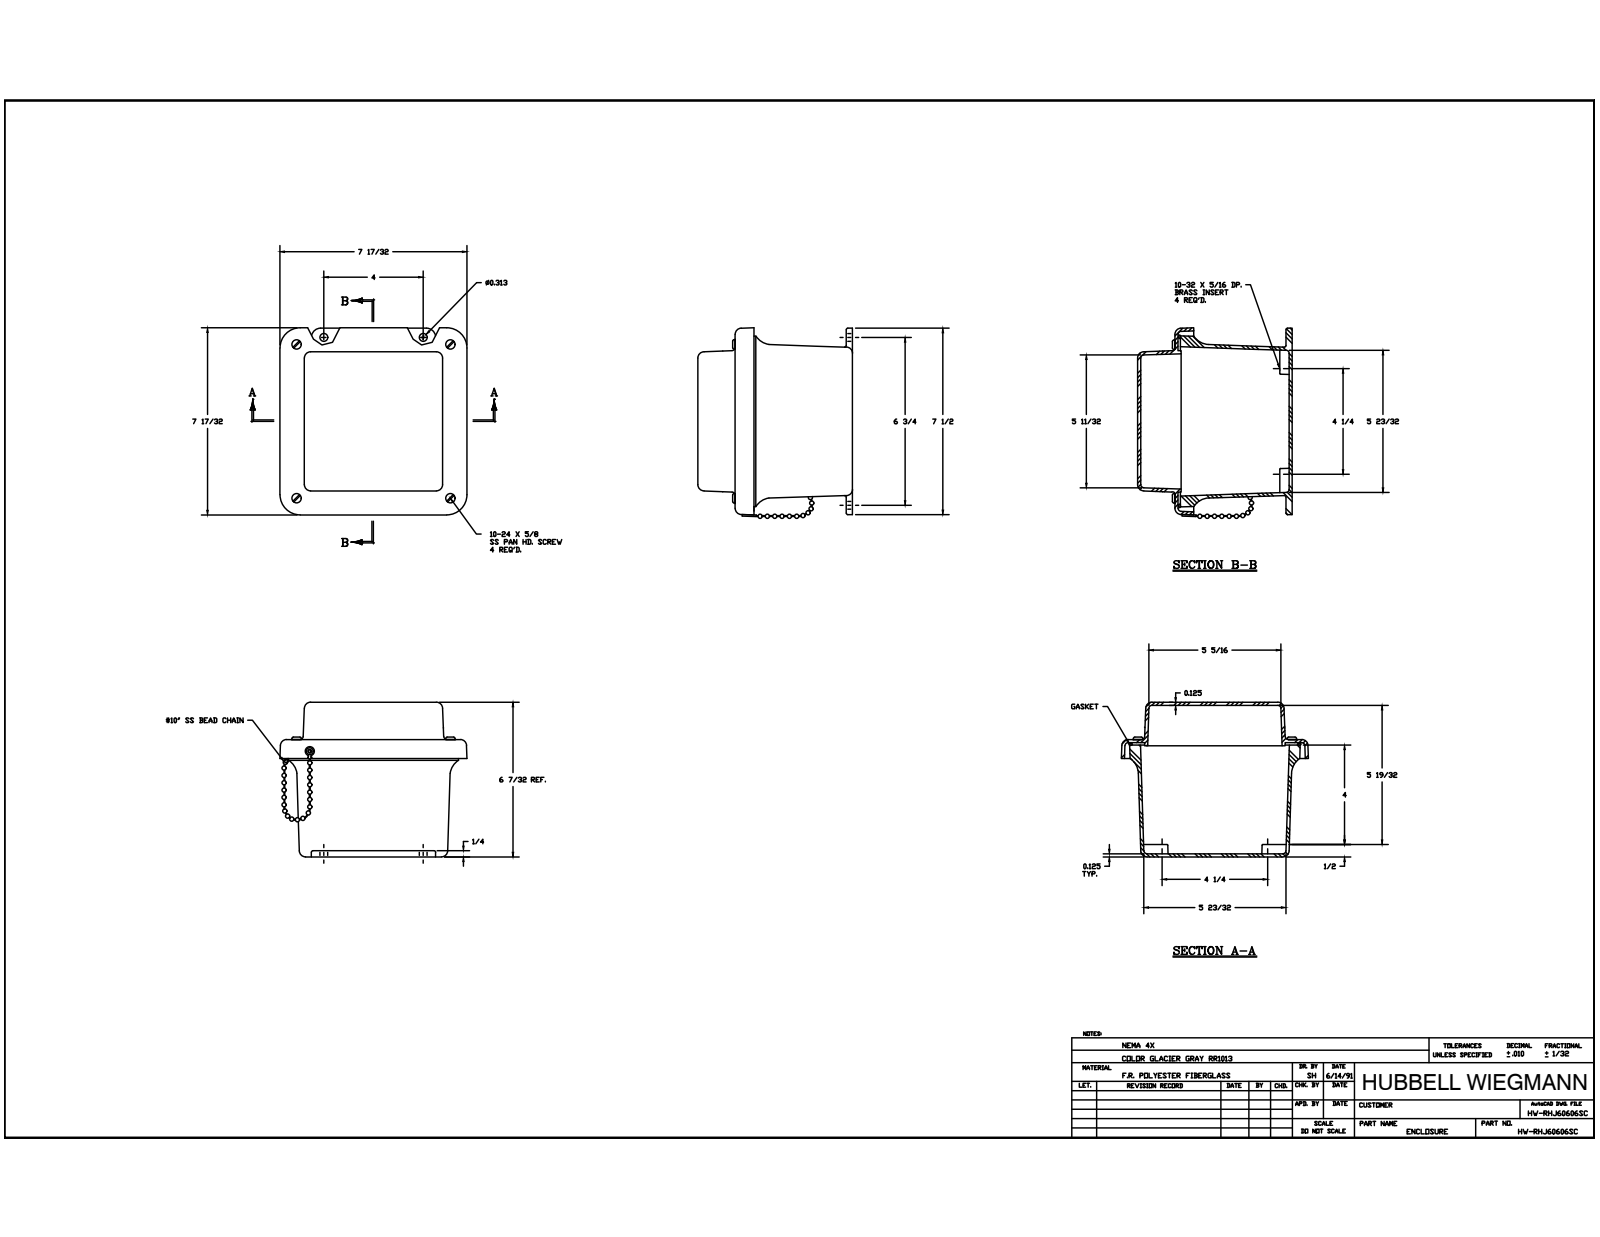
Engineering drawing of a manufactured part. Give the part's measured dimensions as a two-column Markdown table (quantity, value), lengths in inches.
| quantity | value |
| --- | --- |
| part name | J606W_2; RMINS45821P_125; RMINS45821P_126; RMINS45821P_127 (+8 more) |
| STEP written by | Autodesk Inventor 2014 (AUTOMOTIVE_DESIGN) |
| units | inches |
| bodies | 21 solids, 915 faces (208 planar, 301 cylindrical, 406 other) |
| overall size | 8.141 × 7.8 × 6.324 |
| volume | 40.17 in³ |
| surface area | 556.5 in² |
| round holes (diameter × count) | 0.152 × 5, 0.145 × 4, 0.156 × 4, 0.218 × 4, 0.14 × 3, 0.187 × 2, 0.126 × 1 |
| round bosses / shafts (diameter × count) | 0.27 × 8, 0.19 × 4, 0.156 × 4, 0.375 × 2, 0.25 × 2, 0.125 × 2, 0.283 × 1 |
| partial cylindrical surfaces (radius × count) | 0.031 × 20, 0.125 × 16, 0.25 × 16, 0.063 × 4, 0.2 × 4, 0.311 × 4, 0.313 × 4, 0.375 × 4 |
| main face-to-face distances | 0.125, 6.199, 4.699, 1.5, 0.125, 6.324, 6.074, 4.574, 1.625, 4.824 |
| hole center spacings | 5.308, 1.37, 4.25, 6.187, 7.38, 6.01, 8.75, 4 |
